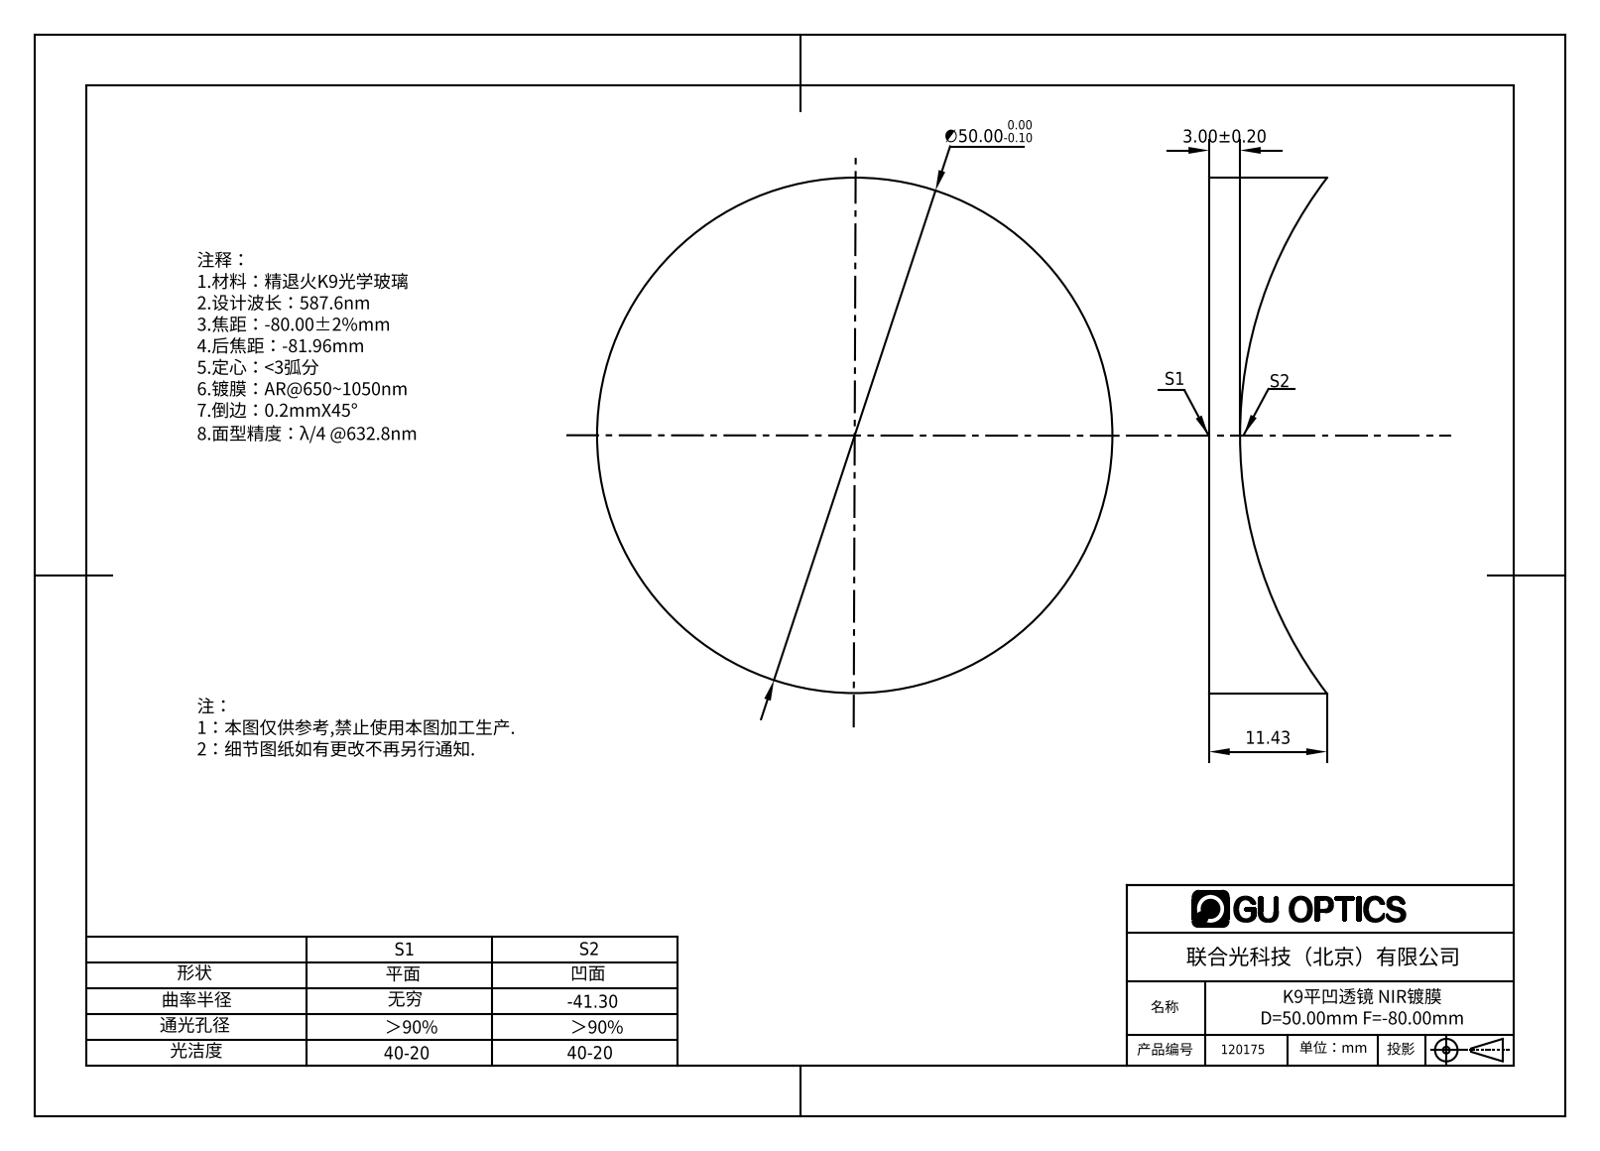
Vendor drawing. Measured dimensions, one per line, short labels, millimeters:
name: 120055
written by: SolidWorks 2016 (AUTOMOTIVE_DESIGN)
unit: mm
bodies: 1 solid, 5 faces (1 planar, 2 cylindrical, 2 other)
size: 50 × 50 × 11.43
volume: 13 850 mm³; area: 5 945 mm²
bosses: 1× ⌀50
